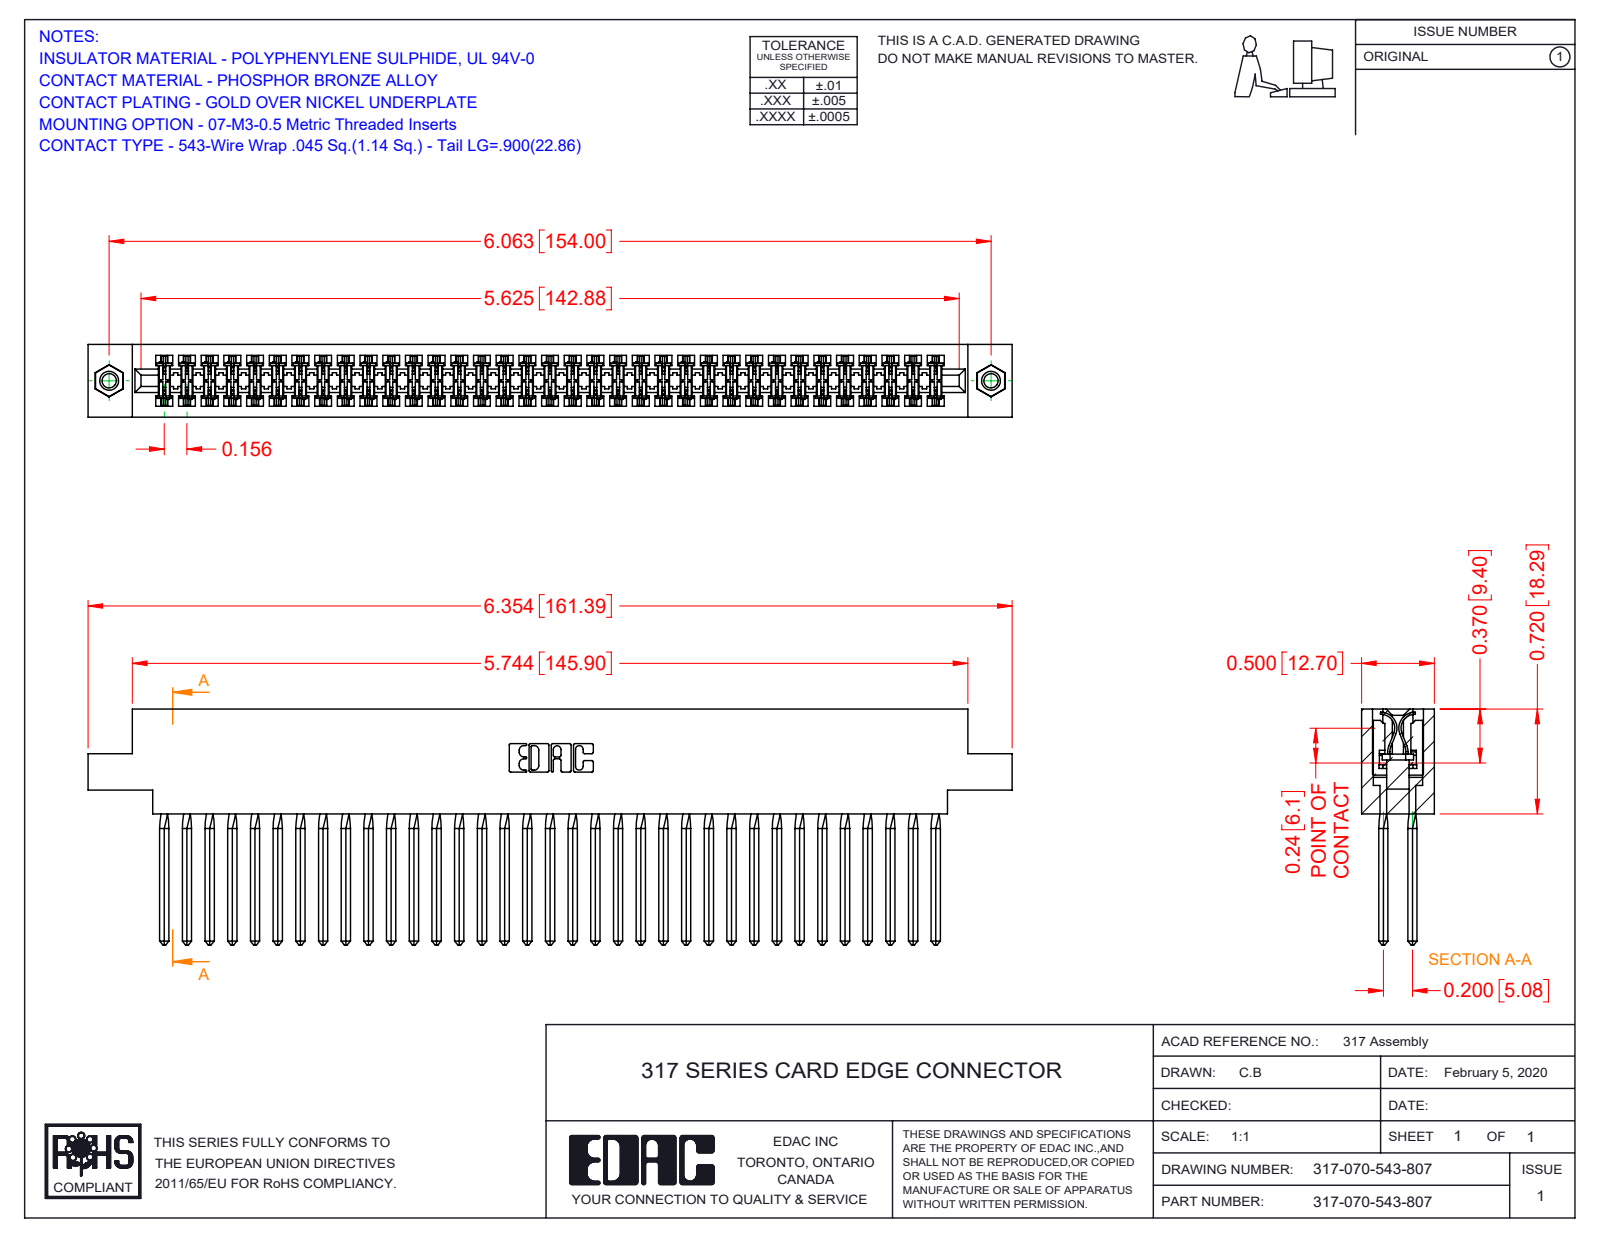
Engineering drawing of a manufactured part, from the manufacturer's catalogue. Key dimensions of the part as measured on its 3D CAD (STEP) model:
Part name (STEP PRODUCT): 317-070-543-807; 317-290-001_543; 345-250-001_345-250-005-103; 317 Part_.156 Dia - TI
STEP written by: SolidWorks 2016 (CONFIG_CONTROL_DESIGN)
Units: inches
Bodies: 73 solids, 6392 faces (5200 planar, 896 cylindrical, 296 other)
Overall size (bounding box): 6.354 × 1.62 × 0.5
Volume: 1.659 in³ · Surface area: 63.55 in²
Round holes (diameter × count): ⌀0.098 ×2, ⌀0.125 ×2, ⌀0.156 ×2
Round bosses / shafts (diameter × count): ⌀0.155 ×2
Partial cylindrical surfaces — rounded edges, fillets, slot ends (radius × count): R0.015 ×140, R0.01 ×22, R0.007 ×6, R0.031 ×6, R0.026 ×3, R0.095 ×2, R0.1 ×2, R0.11 ×2
Main face-to-face distances: 0.5, 0.075, 0.425, 0.35, 0.11, 0.195, 0.094, 0.2, 0.115, 0.131
Hole centre spacings: 6.063
